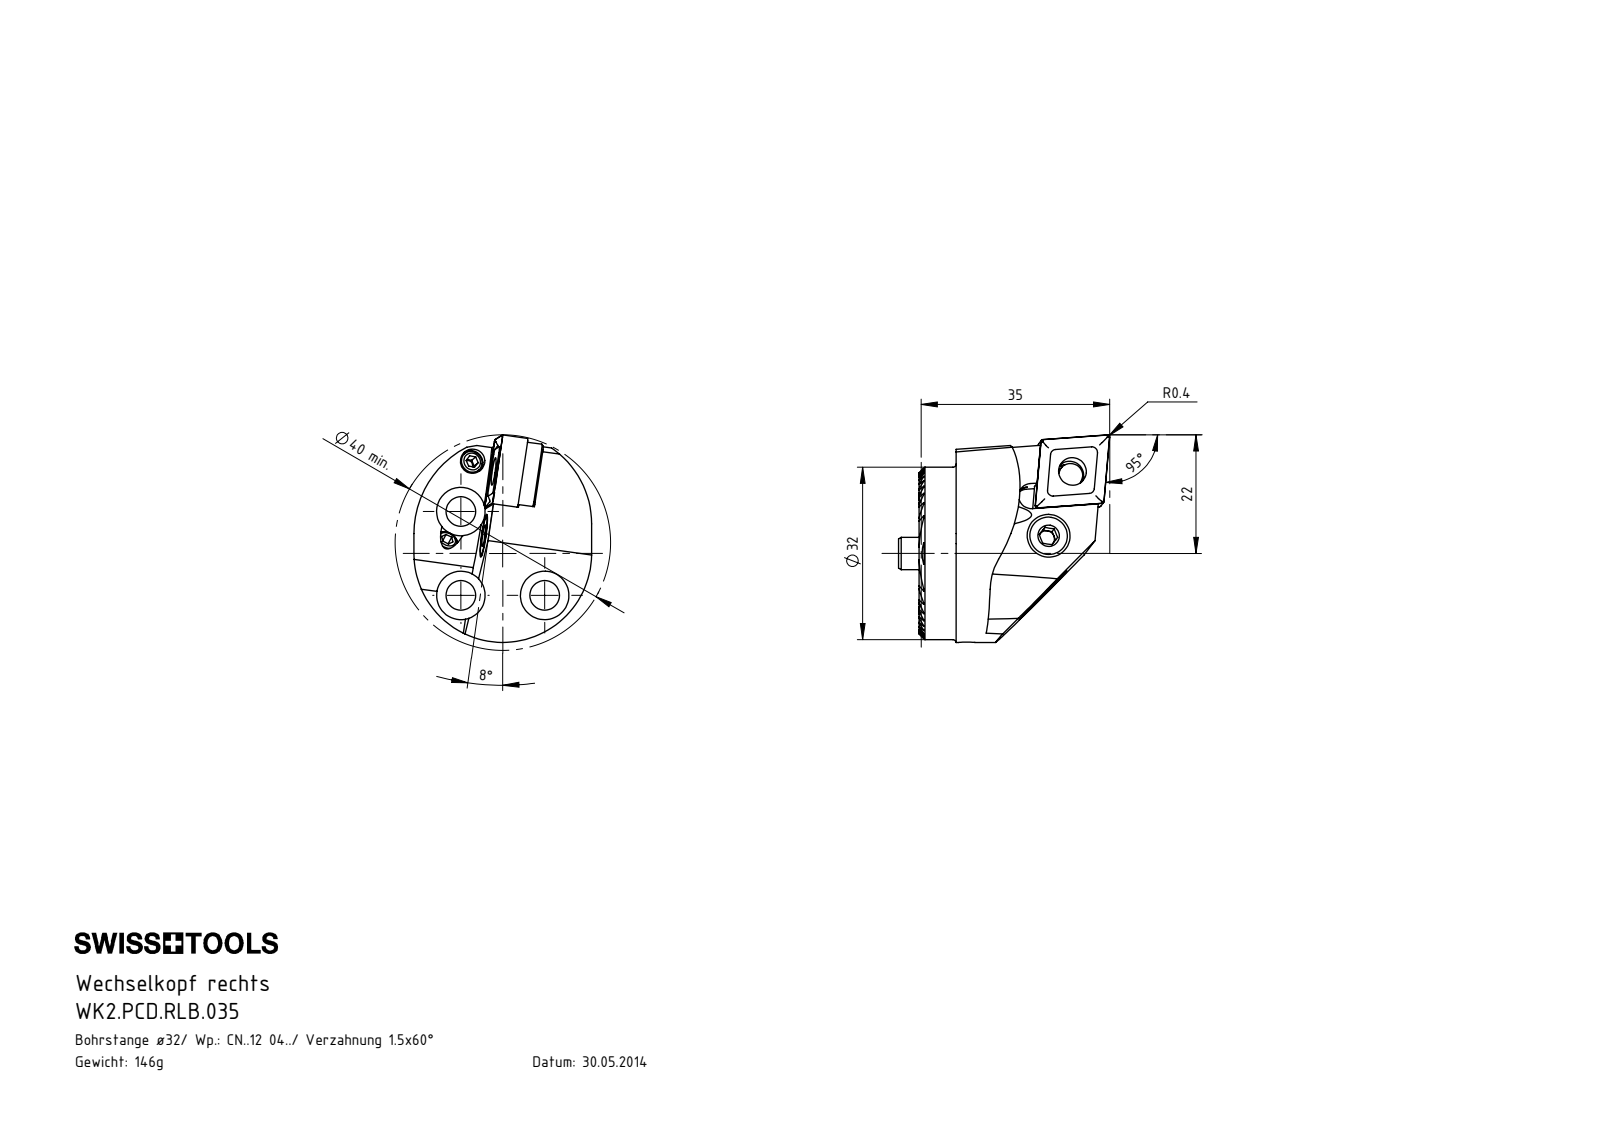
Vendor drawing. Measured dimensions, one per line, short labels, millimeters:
name: WCD-ER2.101.003_A; WCD-ER1.101.000; CNMG120404; WCD-ER3.101.000_A (+6 more)
written by: SolidWorks 2017 (AUTOMOTIVE_DESIGN)
unit: mm
bodies: 15 solids, 631 faces (238 planar, 206 cylindrical, 187 other)
size: 39.2 × 38.5 × 33
volume: 17 809 mm³; area: 10 798 mm²
holes: 3× ⌀2.38, 3× ⌀2.5, 3× ⌀5.5, 3× ⌀9, 2× ⌀1.7, 2× ⌀3.3, 2× ⌀4.5, 1× ⌀3, 1× ⌀4.2, 1× ⌀5.16, 1× ⌀6.4, 1× ⌀7
bosses: 3× ⌀3, 2× ⌀4, 1× ⌀32, 1× ⌀8, 1× ⌀7.9, 1× ⌀6.4, 1× ⌀6, 1× ⌀4.5
rounds: 22× R0.12, 4× R0.4, 4× R1, 2× R2.5, 1× R2.1, 1× R2.2, 1× R2.35, 1× R2.8
face distances: 1.3, 2.6, 3.9, 5.2, 6.5, 12.99, 11.69, 14.29, 7.8, 10.39
hole spacings: 11, 15.56, 12.81, 12.86, 22.01
